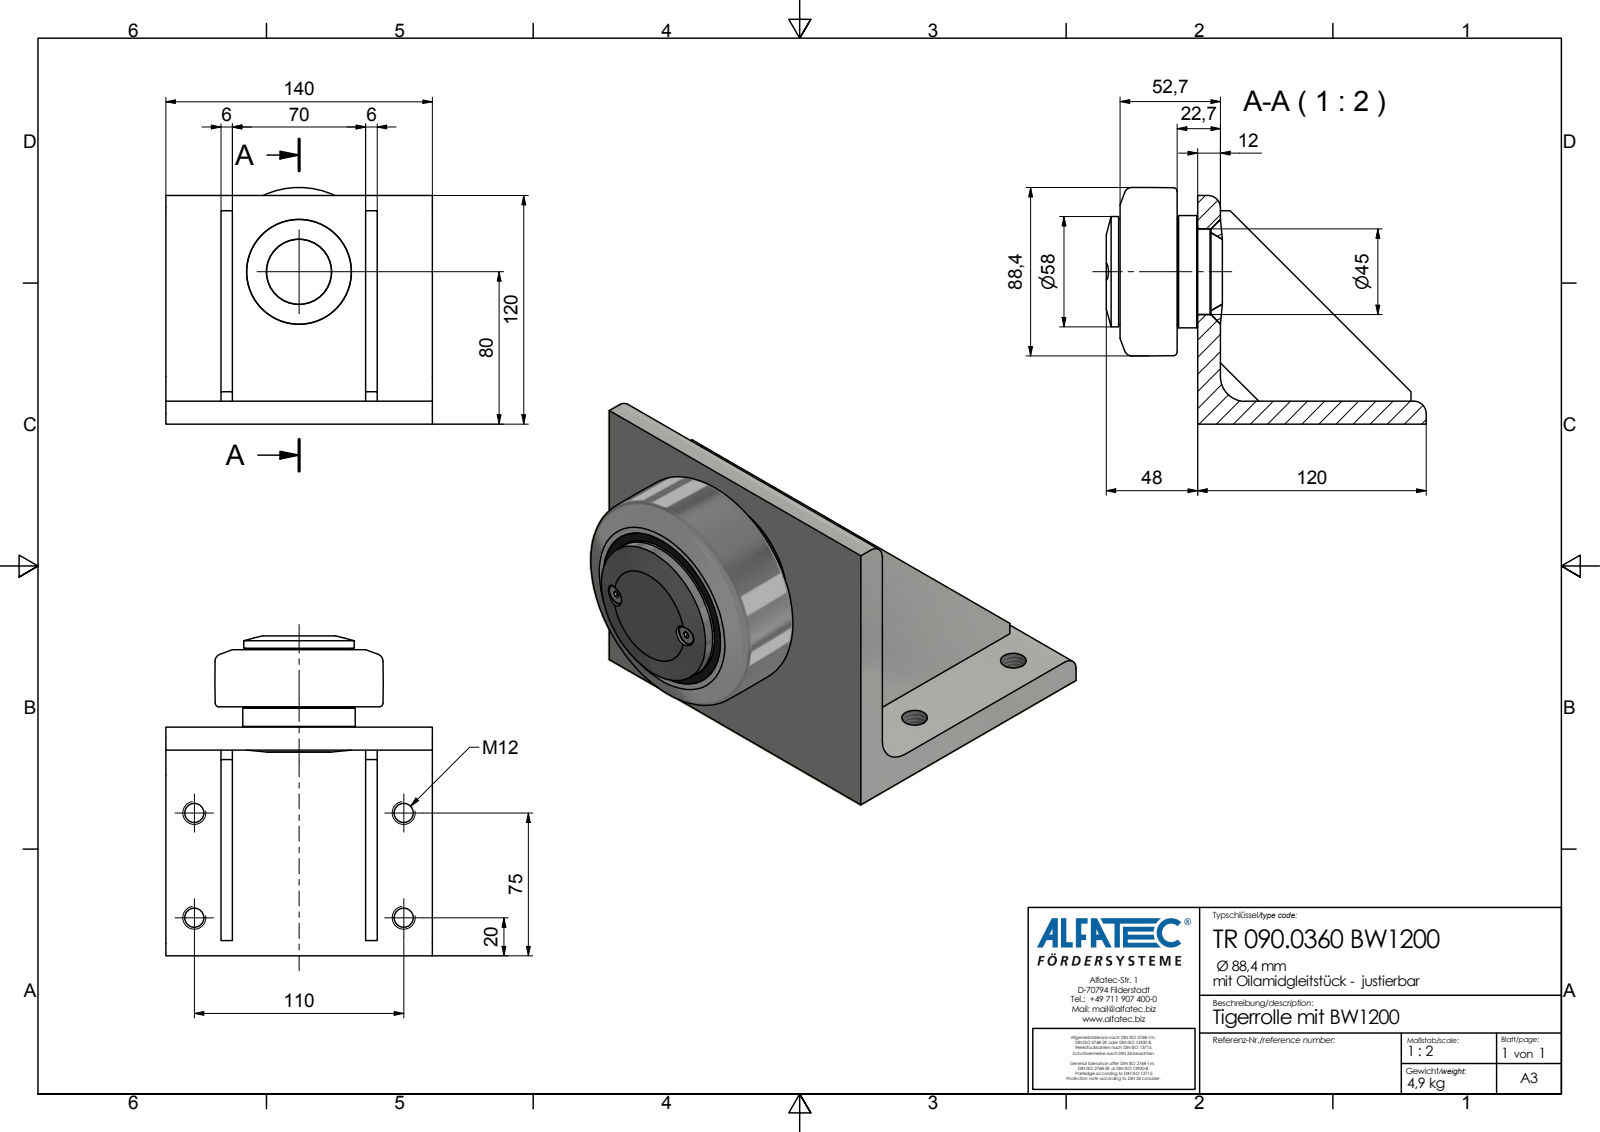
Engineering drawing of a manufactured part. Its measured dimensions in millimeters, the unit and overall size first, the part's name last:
Units: millimetres
Overall size (bounding box): 168 × 140 × 124.2
Round holes (diameter × count): ⌀10.11 ×4, ⌀8.6 ×2
Round bosses / shafts (diameter × count): ⌀7.8 ×2, ⌀59 ×1, ⌀58 ×1, ⌀55.5 ×1, ⌀55.3 ×1
Partial cylindrical surfaces — rounded edges, fillets, slot ends (radius × count): R6.5 ×2, R13 ×1
Main face-to-face distances: 12, 76, 6, 29, 35, 105, 111, 82, 70, 10.7
Hole centre spacings: 55, 110, 122.98, 39
Volume: 672 098 mm³ · Surface area: 111 390 mm²
Bodies: 1 solid, 67 faces (42 planar, 15 cylindrical, 10 other)
Part name (STEP PRODUCT): TR 090.0360 BW1200_Kontur
STEP written by: Autodesk Inventor 2020 (AP242_MANAGED_MODEL_BASED_3D_ENGINEERING_MIM_LF)
